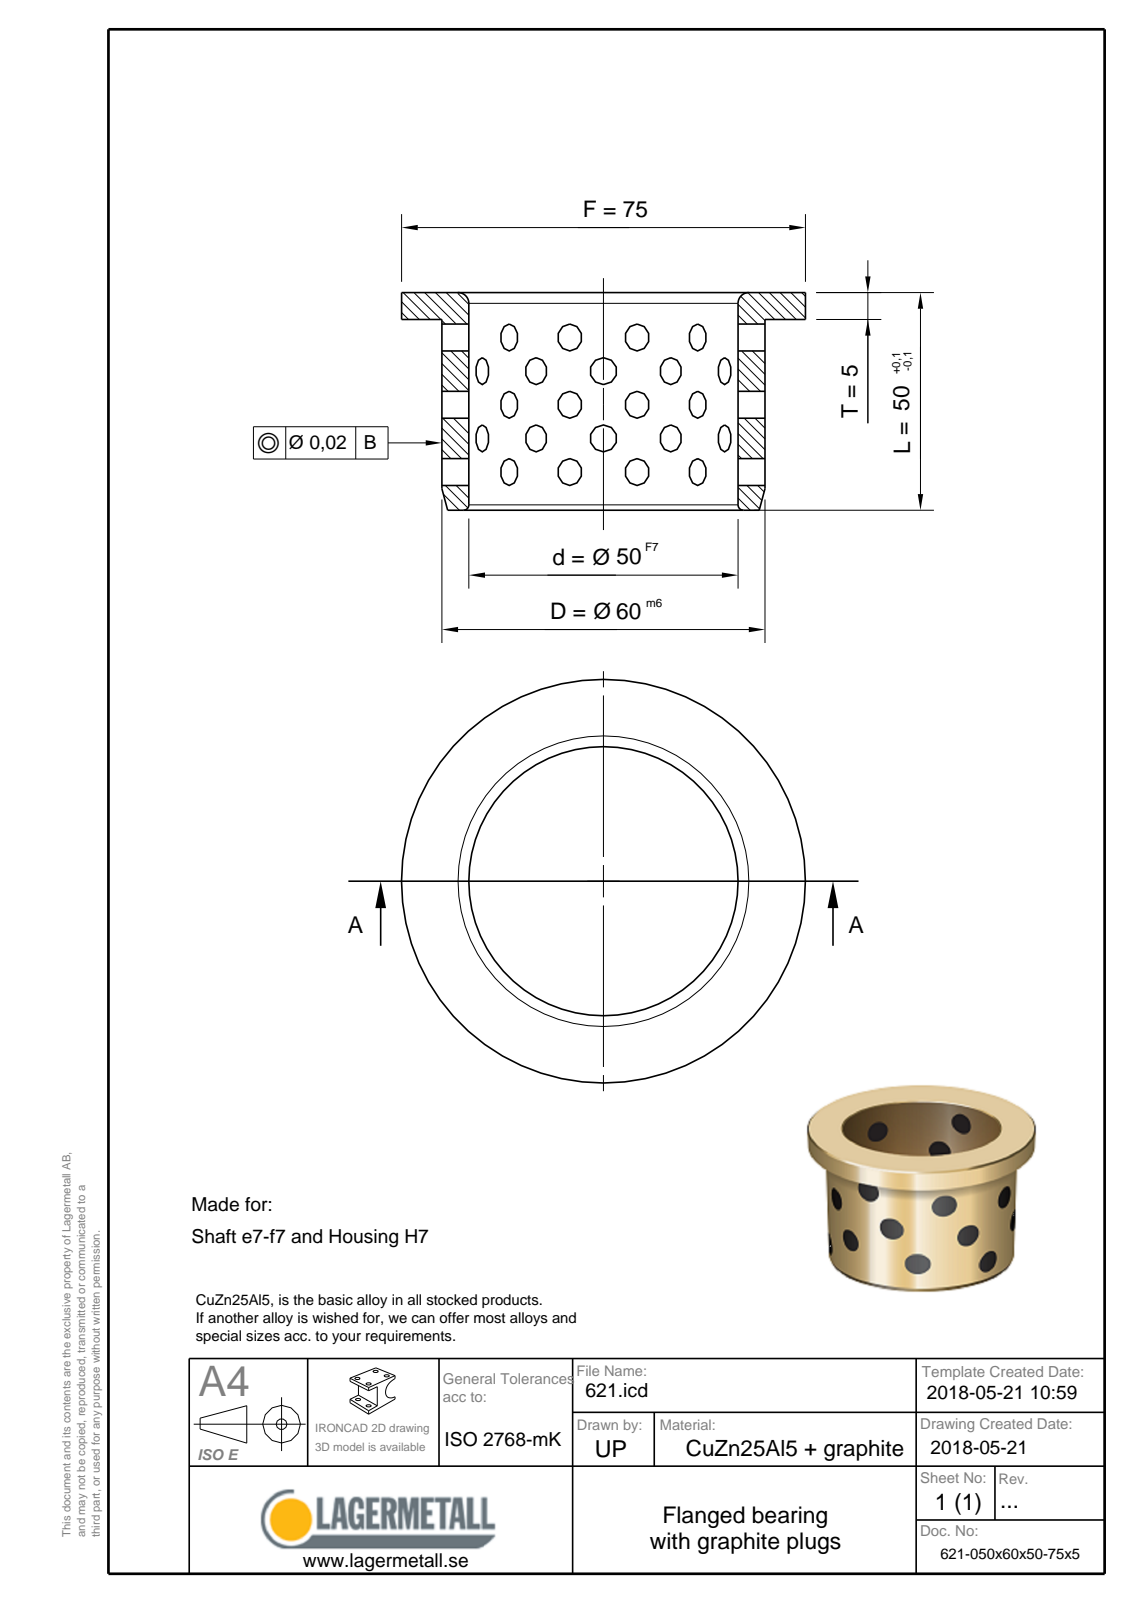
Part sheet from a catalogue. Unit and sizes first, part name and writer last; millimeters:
Units: millimetres
Overall size (bounding box): 75 × 75 × 50
Round holes (diameter × count): ⌀50 ×1
Round bosses / shafts (diameter × count): ⌀75 ×1, ⌀60 ×1
Main face-to-face distances: 5, 45, 50
Volume: 50 653 mm³ · Surface area: 22 024 mm²
Bodies: 1 solid, 9 faces (3 planar, 3 cylindrical, 3 other)
Part name (STEP PRODUCT): 621-050x60x50-75x5
STEP written by: Spatial InterOp 3D (CONFIG_CONTROL_DESIGN)
